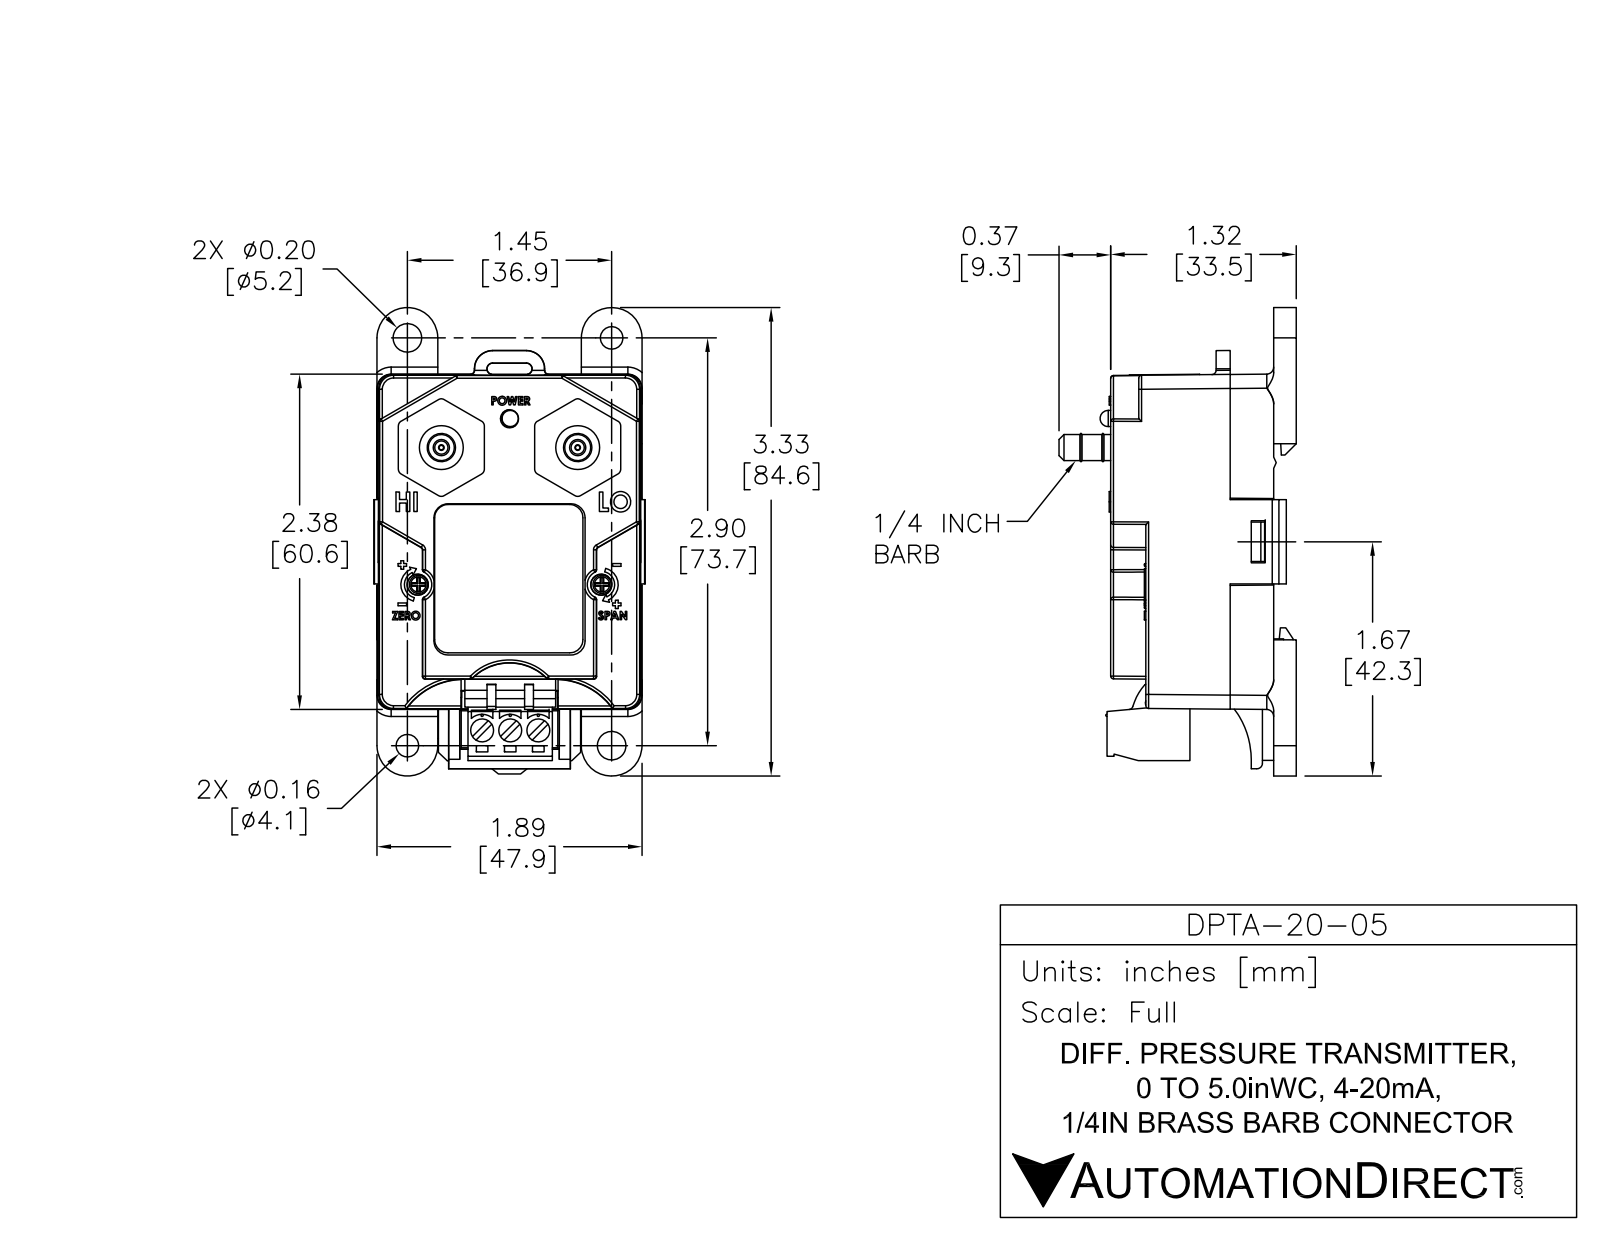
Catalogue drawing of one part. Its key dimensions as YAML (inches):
part_name: "DPTA-20-05"
step_written_by: "SolidWorks 2011 (AUTOMOTIVE_DESIGN)"
units: inches
bodies: {solids: 11, faces: 448, planar: 354, cylindrical: 85, other: 9}
overall_size: [3.347, 1.959, 1.697]
volume: 1.811
surface_area: 53.85
round_holes:
  - {diameter: 0.157, count: 7}
  - {diameter: 0.098, count: 2}
  - {diameter: 0.202, count: 2}
  - {diameter: 0.122, count: 1}
round_bosses_or_shafts:
  - {diameter: 0.197, count: 3}
  - {diameter: 0.138, count: 3}
  - {diameter: 0.138, count: 3}
  - {diameter: 0.315, count: 2}
  - {diameter: 0.187, count: 2}
  - {diameter: 0.118, count: 1}
partial_cylinders:
  - {radius: 0.118, count: 12}
  - {radius: 0.079, count: 4}
  - {radius: 0.217, count: 4}
  - {radius: 0.039, count: 2}
  - {radius: 0.042, count: 2}
  - {radius: 0.044, count: 2}
  - {radius: 0.094, count: 2}
  - {radius: 0.128, count: 2}
face_to_face_distances: [0.039, 0.075, 0.157, 1.146, 0.02, 1.846, 0.232, 0.197, 1.303, 1.071]
hole_center_spacings: [0.533, 0.816, 0.92, 0.981, 1.159, 1.357, 1.444, 1.505]
